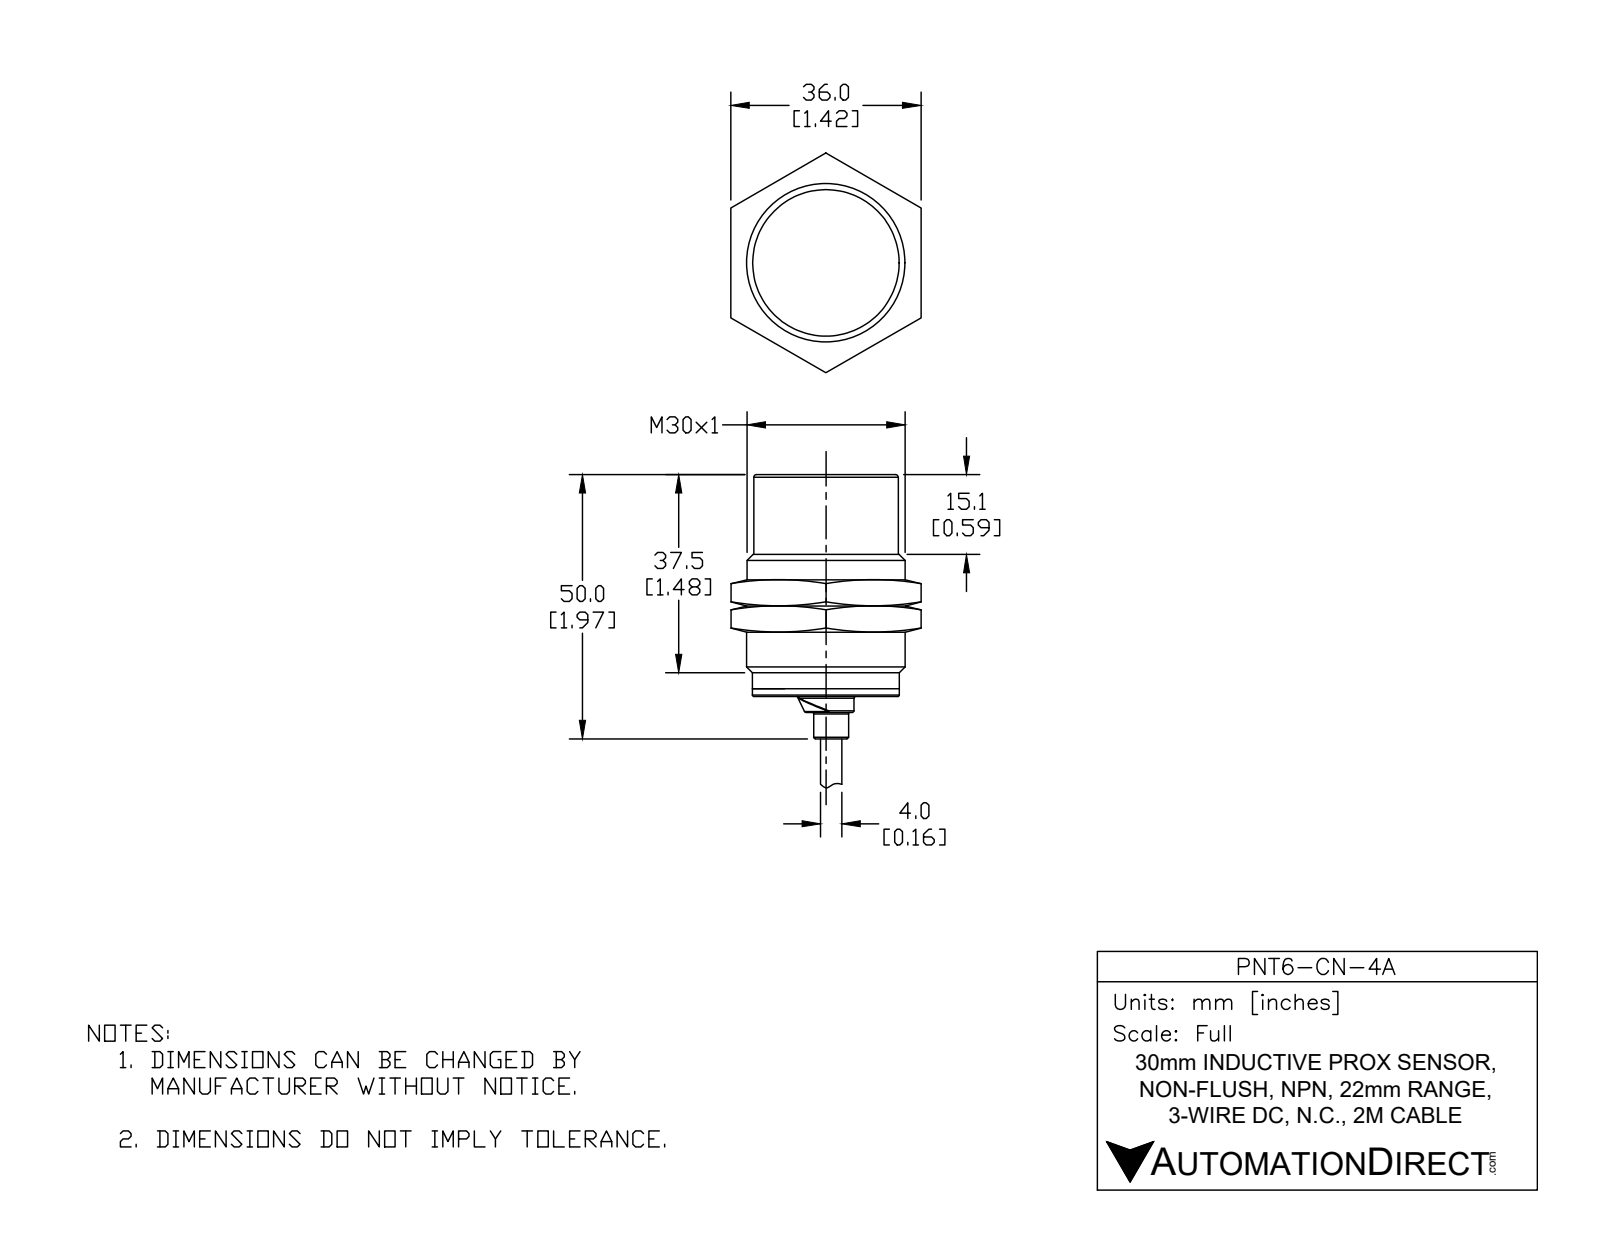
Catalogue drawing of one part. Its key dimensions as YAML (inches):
part_name: "PNT6-CN-4A"
step_written_by: "SolidWorks 2017 (AUTOMOTIVE_DESIGN)"
units: inches
bodies: {solids: 1, faces: 77, planar: 15, cylindrical: 30, other: 32}
overall_size: [3.969, 1.181, 1.181]
volume: 1.84
surface_area: 9.715
round_holes:
  - {diameter: 0.162, count: 1}
round_bosses_or_shafts:
  - {diameter: 0.049, count: 6}
  - {diameter: 1.181, count: 1}
  - {diameter: 1.095, count: 1}
  - {diameter: 1.094, count: 1}
  - {diameter: 0.417, count: 1}
  - {diameter: 0.26, count: 1}
  - {diameter: 0.157, count: 1}
partial_cylinders:
  - {radius: 0.077, count: 1}
face_to_face_distances: [1.654, 1.772, 0.118, 1.969, 0.315, 0.197, 3.969, 2.315, 2.197, 2]
